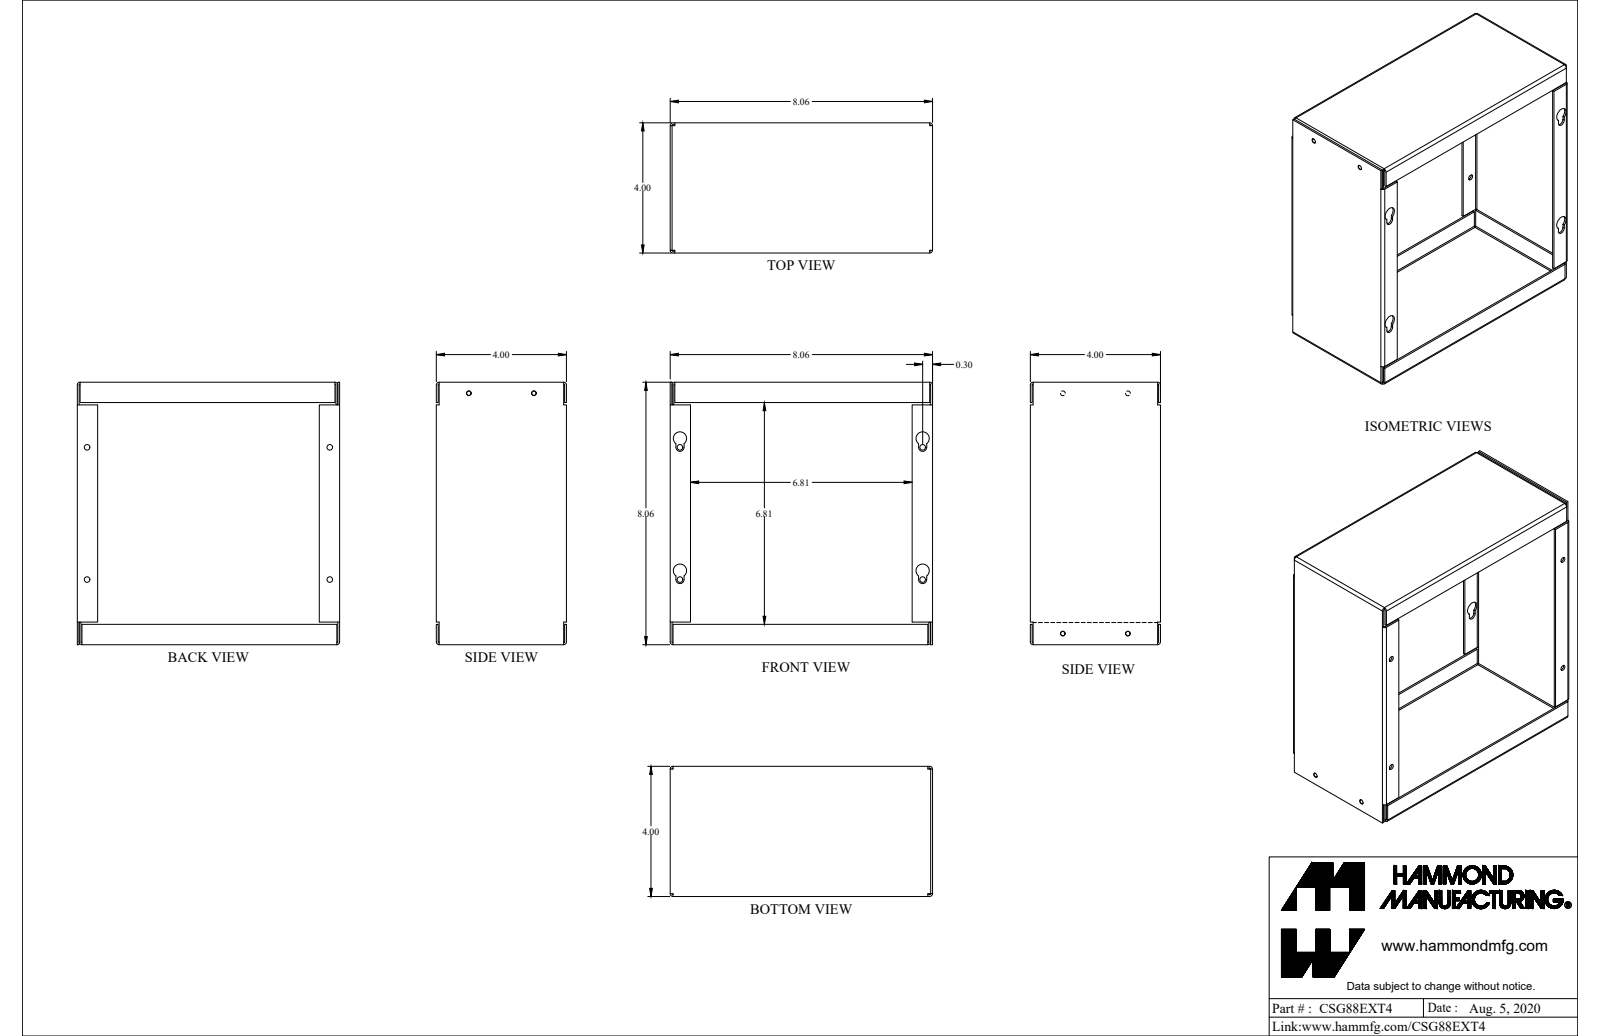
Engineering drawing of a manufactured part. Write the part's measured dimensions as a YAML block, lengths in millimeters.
part_name: "CSG88EXT4"
step_written_by: "SolidWorks 2021 (AUTOMOTIVE_DESIGN)"
units: millimeters
bodies: {solids: 2, faces: 124, planar: 80, cylindrical: 44, other: 0}
overall_size: [204.8, 204.8, 101.6]
volume: 152000
surface_area: 213700
round_holes:
  - {diameter: 3.7, count: 4}
  - {diameter: 4.3, count: 4}
round_bosses_or_shafts:
  - {diameter: 3.3, count: 4}
partial_cylinders:
  - {radius: 0.7, count: 12}
  - {radius: 2.2, count: 12}
  - {radius: 3.2, count: 4}
  - {radius: 5.2, count: 4}
face_to_face_distances: [203.4, 1.4, 1.4, 201.9, 204.8, 204.8, 201.9, 100.2, 98.7, 101.6]
hole_center_spacings: [50.8, 103.2, 187.5, 189.5, 194.2, 215.7]
